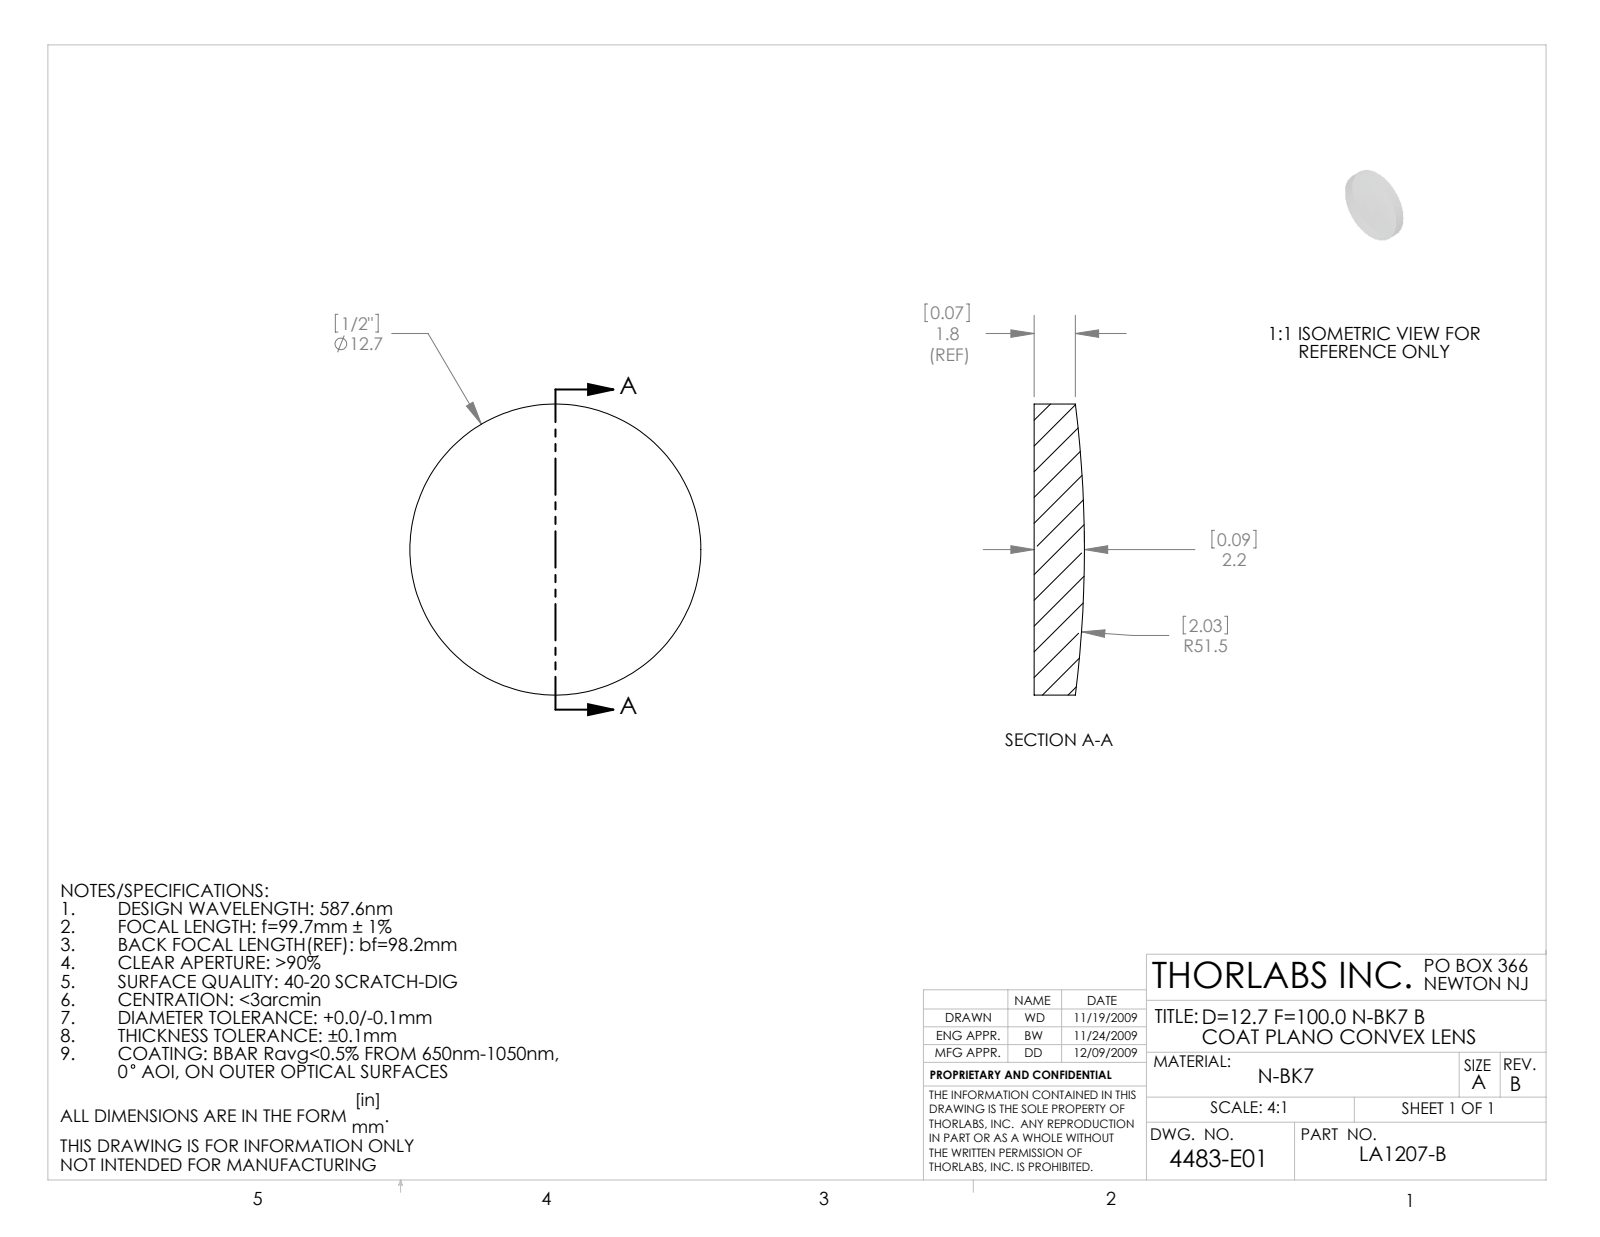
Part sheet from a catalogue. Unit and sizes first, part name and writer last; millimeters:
Units: millimetres
Overall size (bounding box): 12.7 × 12.7 × 2.19
Round bosses / shafts (diameter × count): ⌀12.7 ×1
Volume: 253 mm³ · Surface area: 326 mm²
Bodies: 1 solid, 5 faces (1 planar, 2 cylindrical, 2 other)
Part name (STEP PRODUCT): 4483-E0W
STEP written by: SolidWorks 2009 (AUTOMOTIVE_DESIGN)
